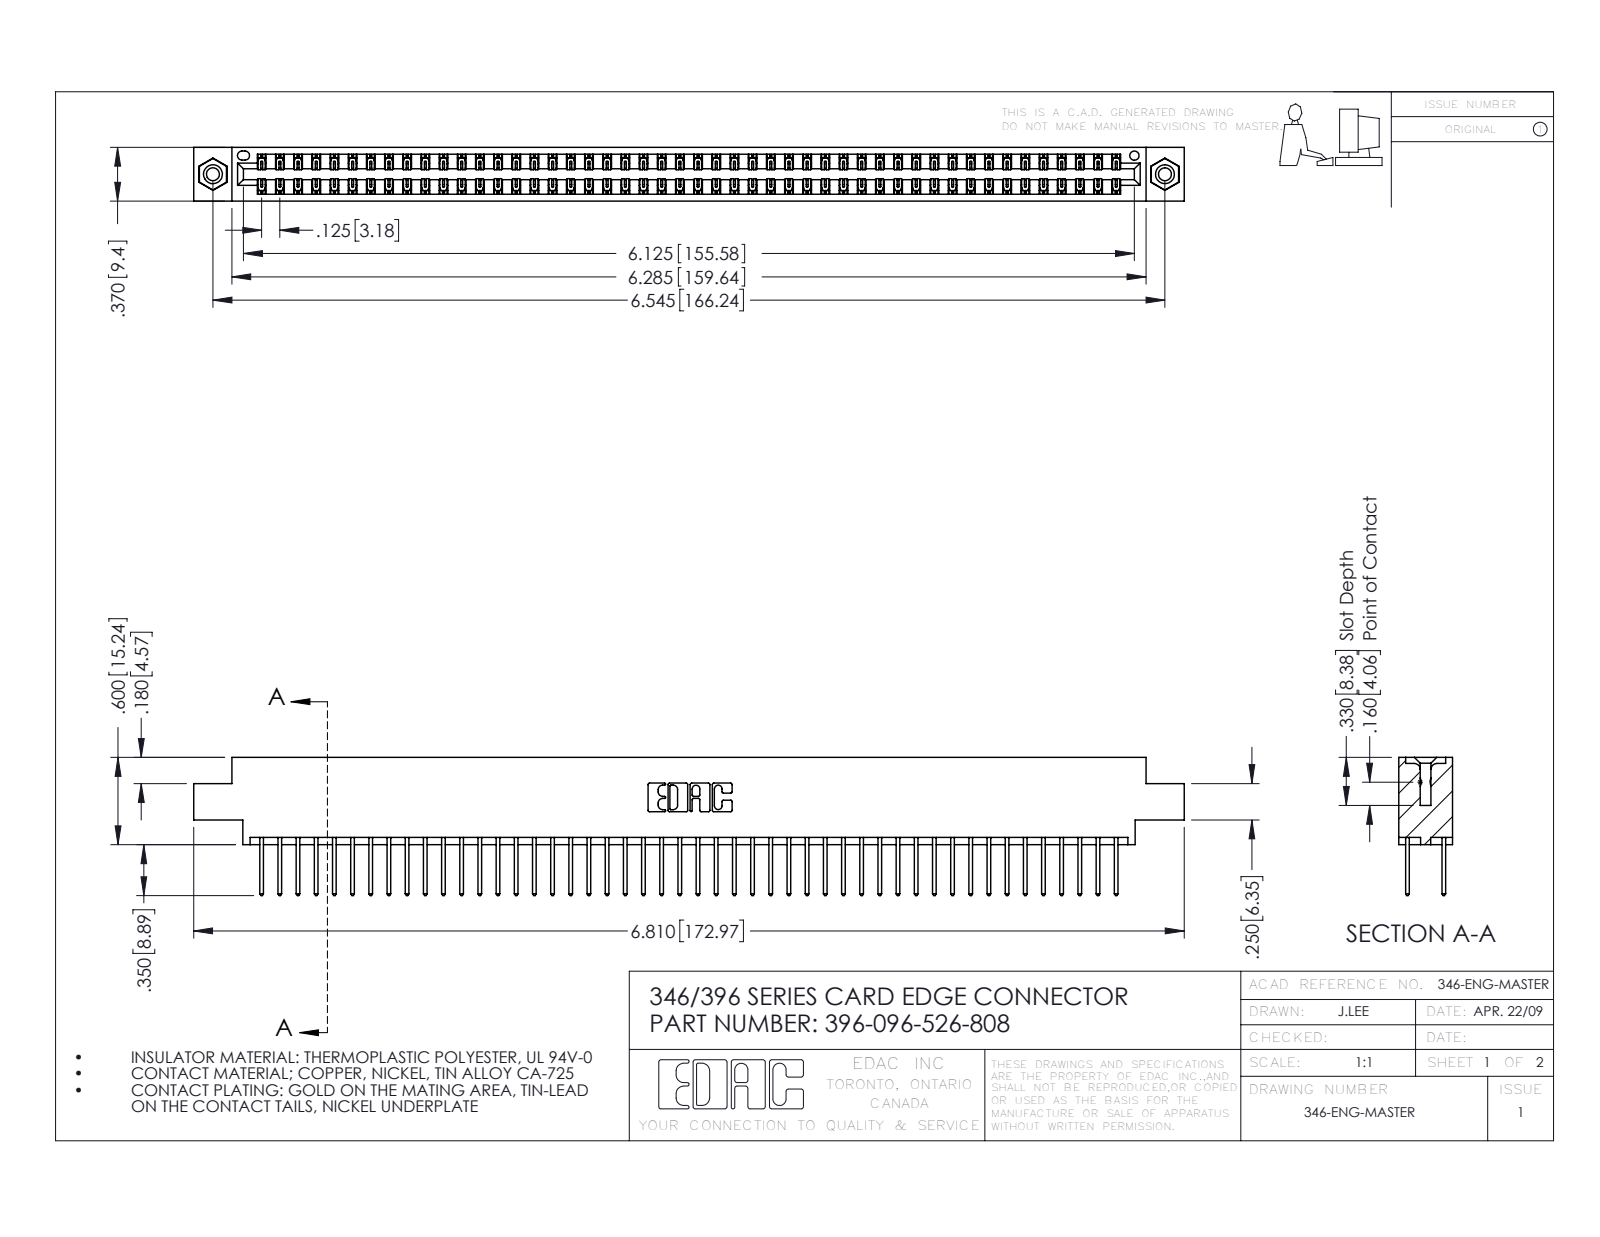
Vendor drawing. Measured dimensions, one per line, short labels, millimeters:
name: 345-292-001_345-293-126; 346 Part_0.170 Offset - 0.156 Dia-TI; 396-096-526-808; 345-250-001_345-250-003-102
written by: SolidWorks 2016 (CONFIG_CONTROL_DESIGN)
unit: mm
bodies: 99 solids, 5178 faces (3472 planar, 1690 cylindrical, 16 other)
size: 173 × 24.1 × 9.4
volume: 16 910 mm³; area: 24 250 mm²
holes: 2× ⌀2.3, 2× ⌀3.2, 2× ⌀4, 1× ⌀1.6
bosses: 2× ⌀3.9
rounds: 144× R0.2, 96× R0.3, 22× R0.3, 6× R0.2, 6× R0.8, 3× R0.7, 2× R0.4, 2× R0.6
face distances: 1.2, 8.2, 6.4, 9.4, 1.8, 7.6, 0.6, 7, 5.6, 3.8
hole spacings: 6.2, 160.9, 166.2
